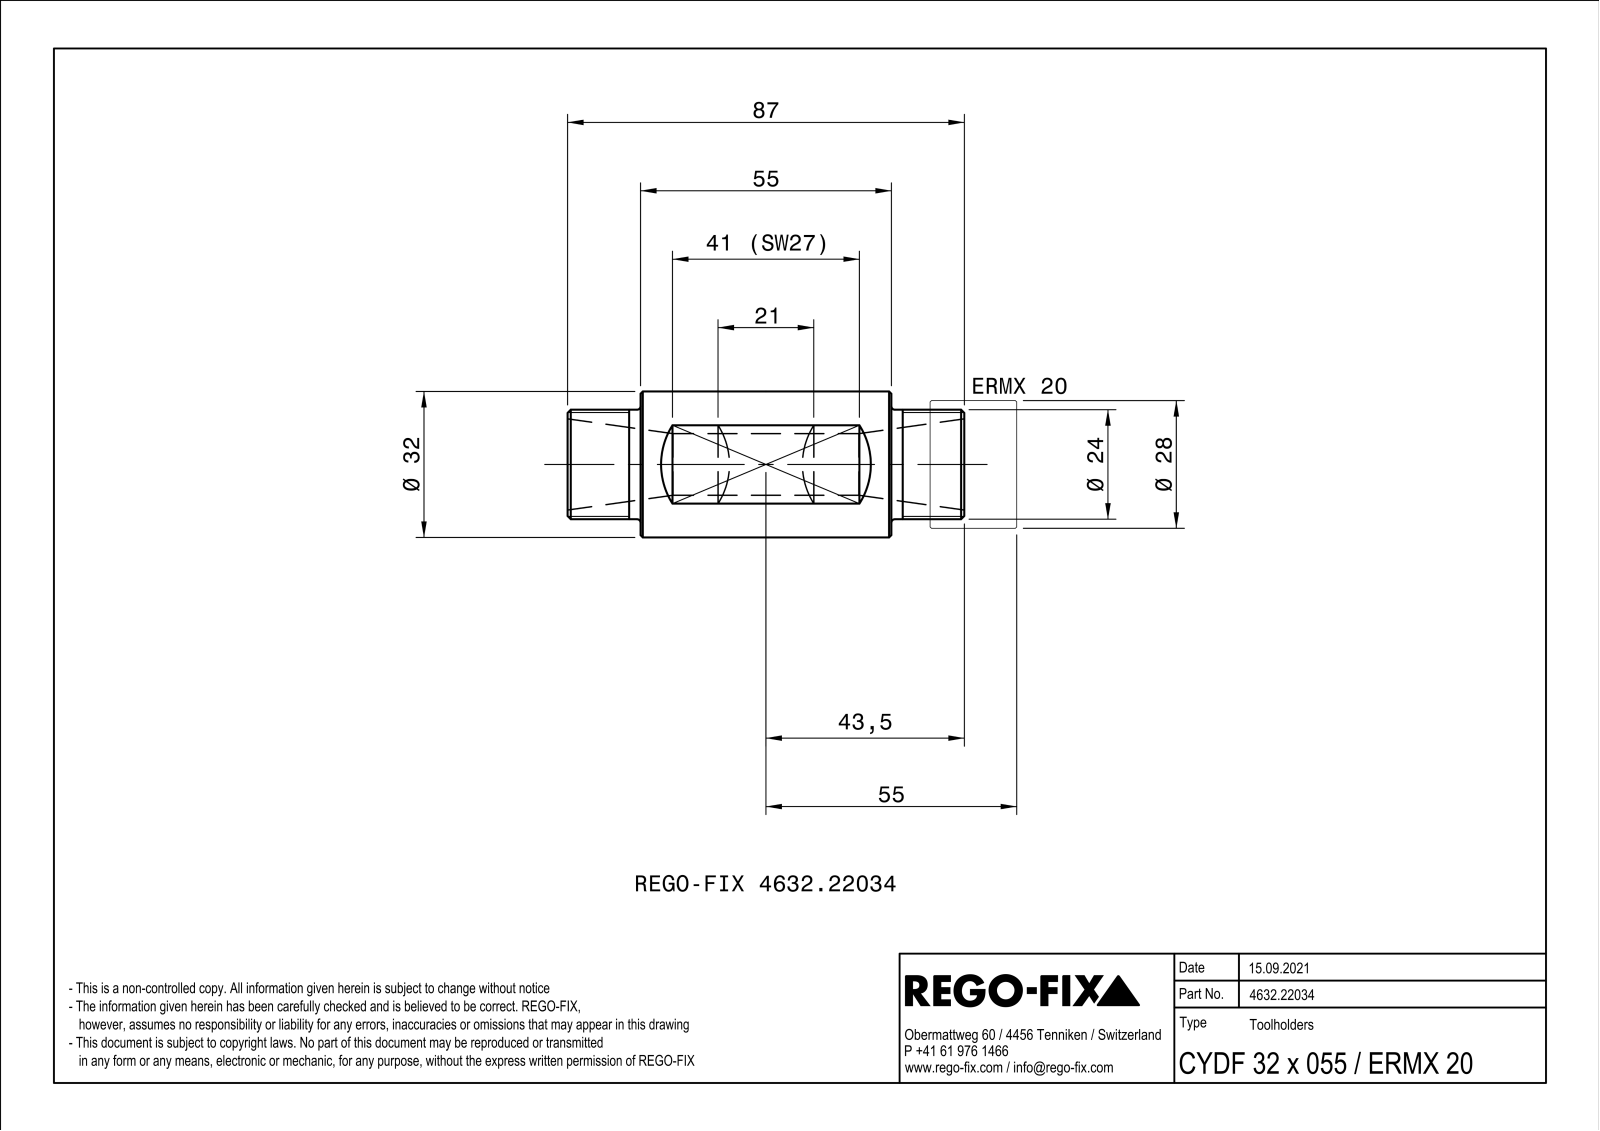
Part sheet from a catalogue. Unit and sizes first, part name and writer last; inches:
Units: inches
Overall size (bounding box): 3.425 × 1.26 × 1.26
Round holes (diameter × count): ⌀0.531 ×1
Round bosses / shafts (diameter × count): ⌀1.26 ×1, ⌀0.945 ×1
Main face-to-face distances: 1.063, 2.165, 0.63, 2.795, 0.473, 0.863, 0.39, 3.425
Volume: 2.475 in³ · Surface area: 20.04 in²
Bodies: 1 solid, 29 faces (13 planar, 6 cylindrical, 10 other)
Part name (STEP PRODUCT): NOCUT
STEP written by: SIEMENS PLM Software Solid Edge ST10 (AUTOMOTIVE_DESIGN)
